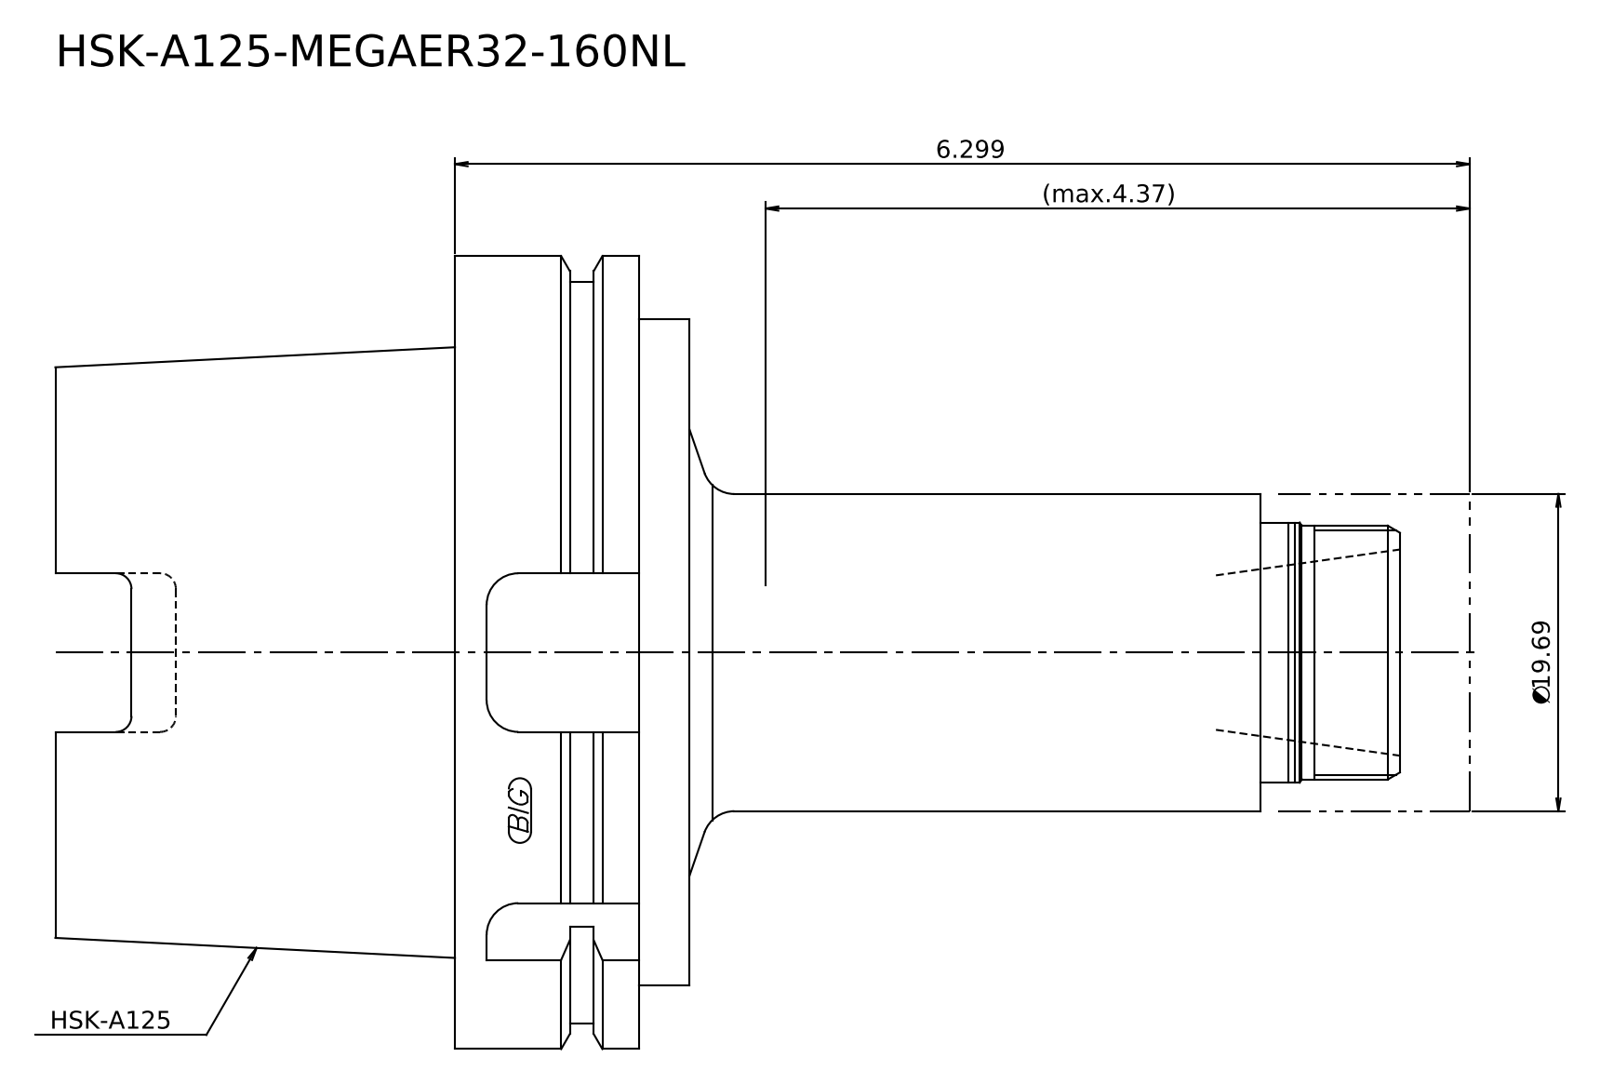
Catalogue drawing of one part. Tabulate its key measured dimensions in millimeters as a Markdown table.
| quantity | value |
| --- | --- |
| STEP written by | Kubotek KeyCreator 2011 V10.0.2 (22737) (automotive_design) |
| units | millimeters |
| bodies | 2 solids, 24 faces (10 planar, 8 cylindrical, 6 other) |
| overall size | 223 × 125 × 125 |
| volume | 1 118 000 mm³ |
| surface area | 83 011 mm² |
| round bosses / shafts (diameter × count) | 125 × 1, 117 × 1, 105 × 1, 50 × 1, 41 × 1, 40 × 1 |
| main face-to-face distances | 63, 37, 100, 8, 29, 92, 30.2, 123, 131, 160 |
